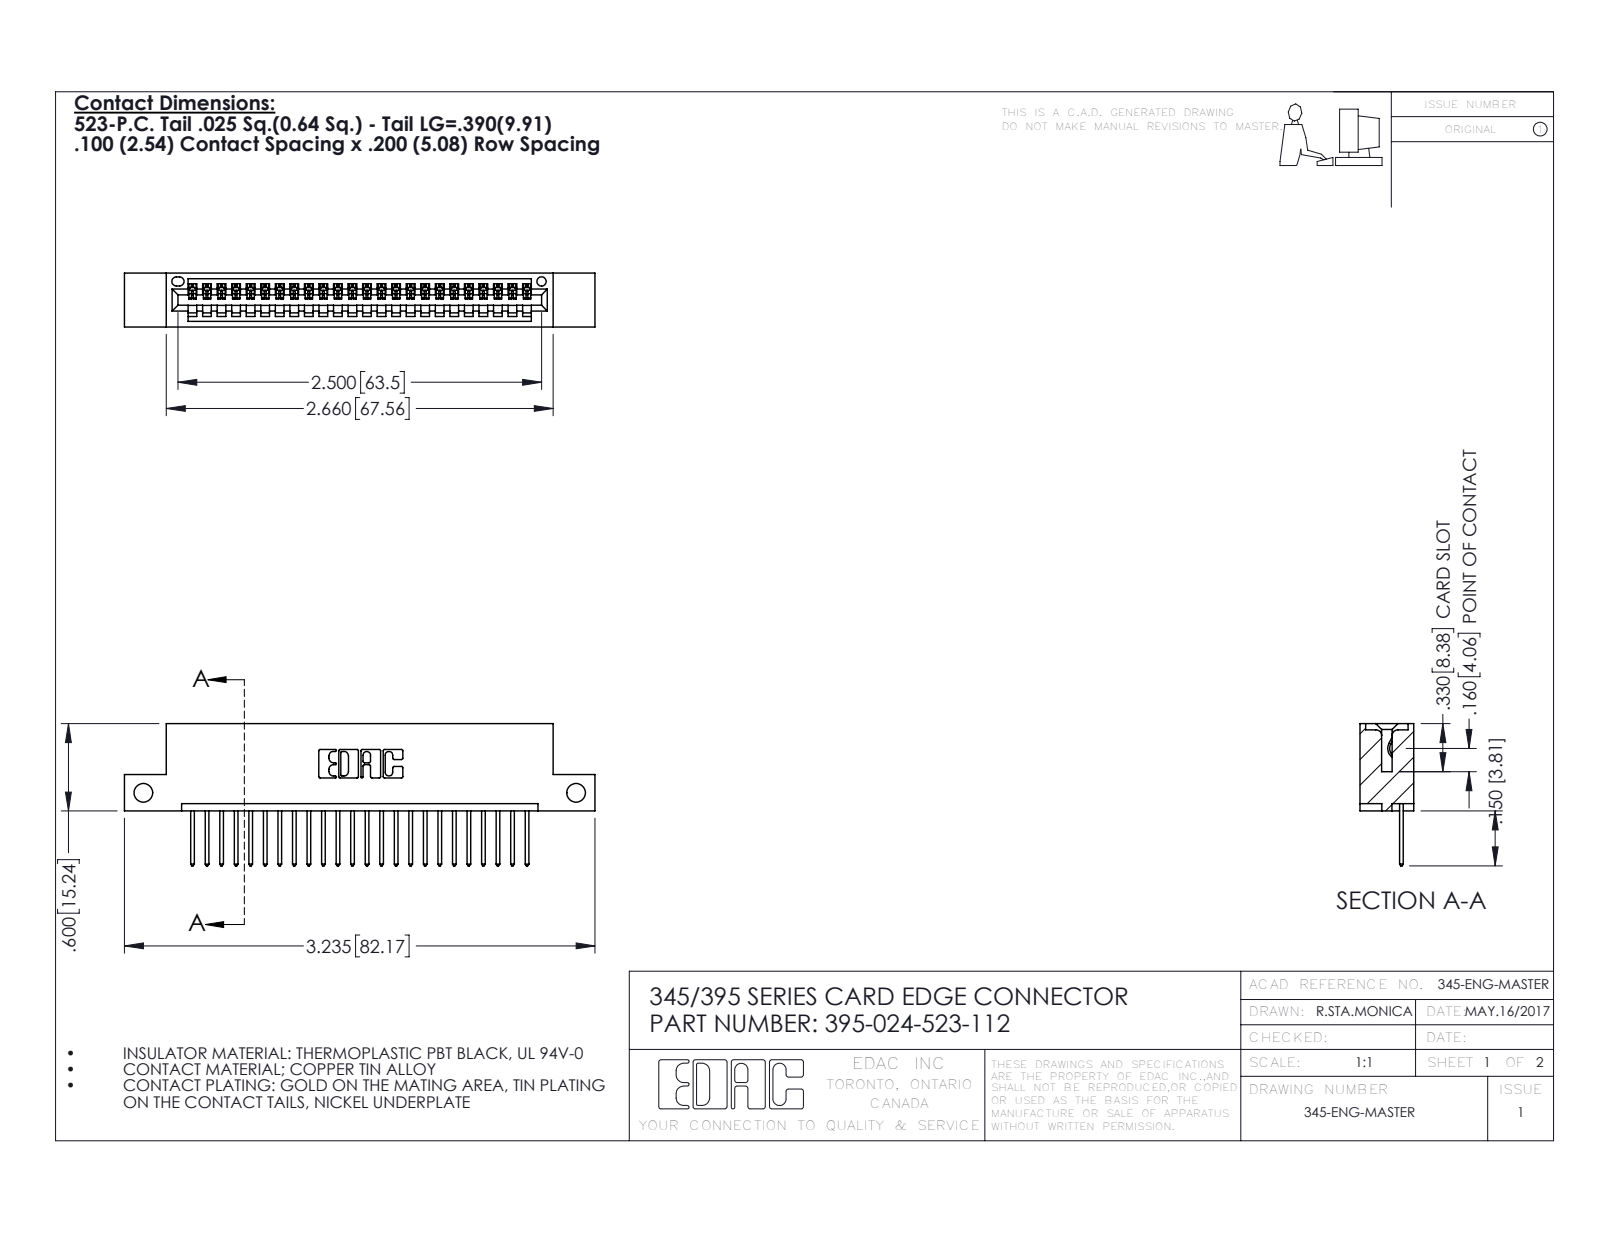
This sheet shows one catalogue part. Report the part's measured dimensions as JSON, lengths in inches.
{"part_name": "395-024-523-112; 345-292-001_345-293-123; 345 Part_Flush Mounting Lugs - Side Mount", "step_written_by": "SolidWorks 2016 (CONFIG_CONTROL_DESIGN)", "units": "inches", "bodies": {"solids": 25, "faces": 1518, "planar": 1040, "cylindrical": 478, "other": 0}, "overall_size": [3.235, 0.977, 0.37], "volume_in3": 0.461, "surface_area_in2": 15.01, "round_holes": [[0.128, 2], [0.064, 1]], "partial_cylinders_radius": [[0.006, 48], [0.01, 48], [0.01, 22], [0.007, 6], [0.031, 6], [0.026, 3], [0.031, 2], [0.04, 2]], "face_to_face_distances": [0.298, 0.072, 0.2, 0.37, 0.098, 0.272, 0.025, 0.225, 0.149, 0.072], "hole_center_spacings": [2.975]}
